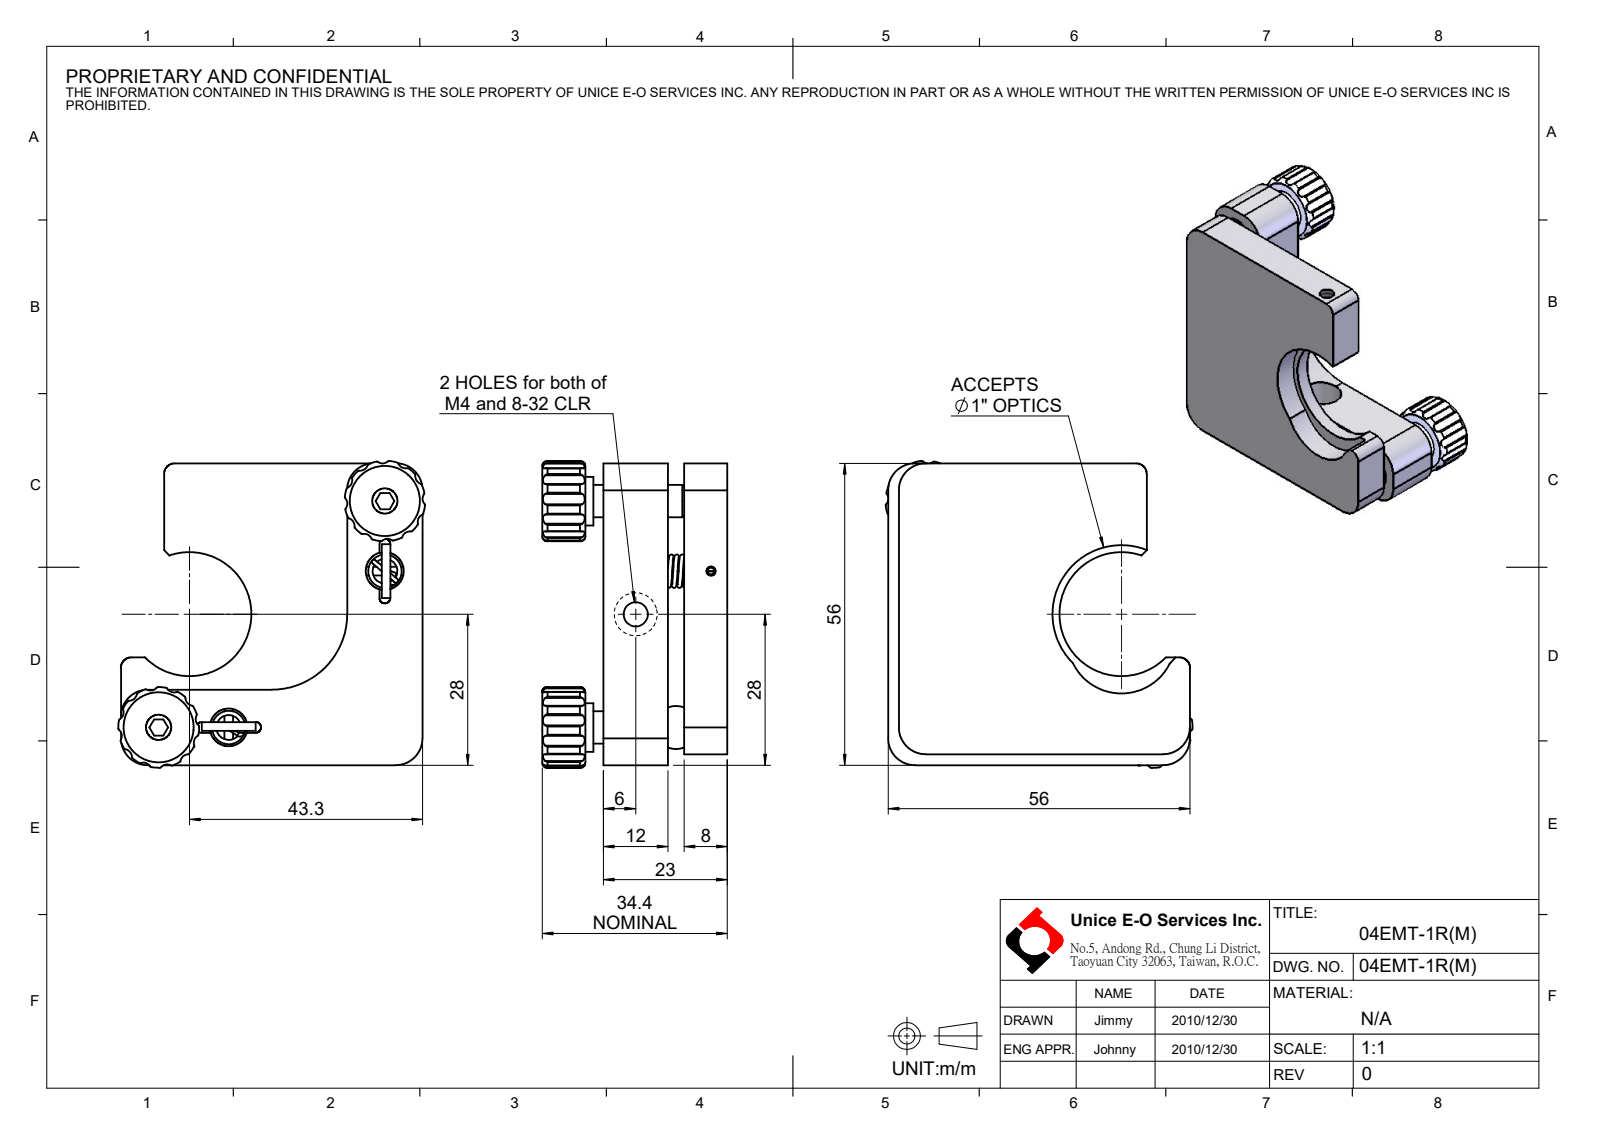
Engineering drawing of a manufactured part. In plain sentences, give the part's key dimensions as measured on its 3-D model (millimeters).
The part is named "04EMT-1R(M)". Its 3-D file was written by "SolidWorks 2016 (CONFIG_CONTROL_DESIGN)". It is 21 solids with 415 faces: 114 planar, 228 cylindrical and 73 other. Overall it measures 56.96 by 56.96 by 34.5 millimeters. Its volume is 35 294 cubic millimeters and its surface area 19 679 square millimeters. Round holes: 4 of diameter 1.2, 2 of diameter 1.7, 2 of diameter 4, 2 of diameter 4.5, 2 of diameter 4.7, 2 of diameter 5.9, 2 of diameter 6, 2 of diameter 7, 2 of diameter 8, 2 of diameter 9.5, 1 of diameter 3.3. Round bosses or shafts: 4 of diameter 1.6, 2 of diameter 9, 2 of diameter 1.5, 2 of diameter 0.8, 1 of diameter 4, 1 of diameter 2.5. Partial cylindrical surfaces (rounded edges, fillets, slot ends): 48 of radius 0.3, 25 of radius 1.5, 8 of radius 5, 4 of radius 0.75, 4 of radius 1, 2 of radius 2, 2 of radius 7.5, 1 of radius 10. The main face-to-face distances are 8, 12, 3, 15, 23, 11, 2, 14, 56, 54. The hole center spacings are 13, 16.12, 51.04, 7.3, 20.87, 21.24, 21.63, 34.12.
